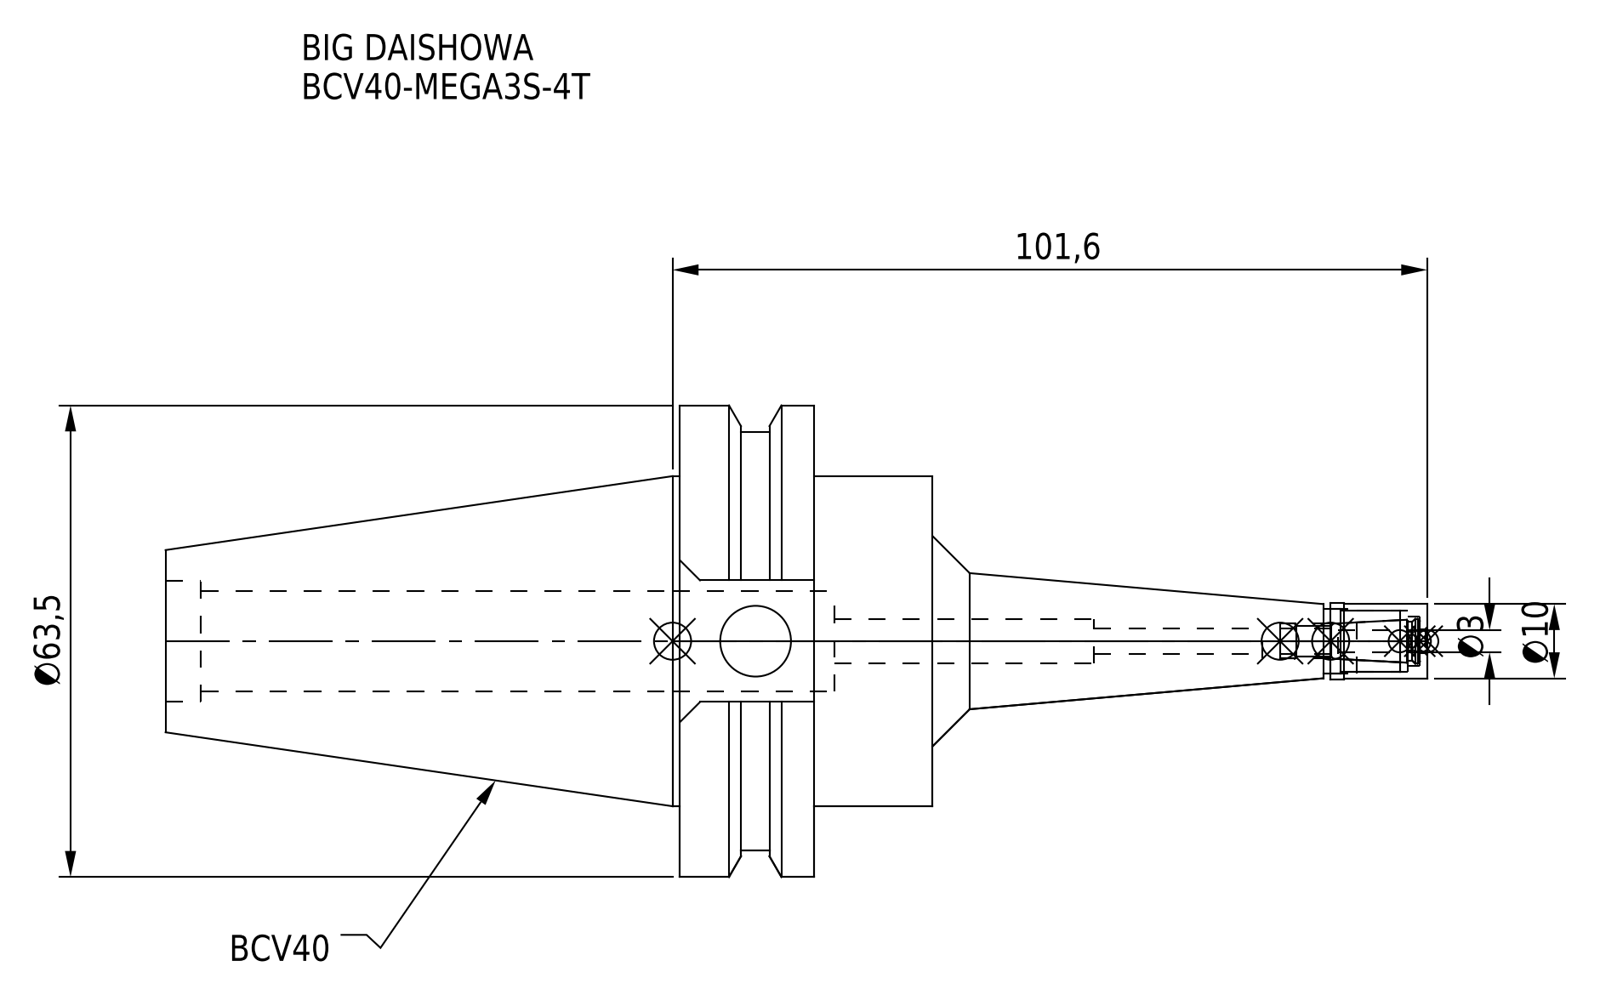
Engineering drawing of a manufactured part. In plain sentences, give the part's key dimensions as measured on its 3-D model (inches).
The part is named "BCV40-MEGA3S-4T-030.stp; BCV40-MEGA3S-4T_1.stp; BCV40-MEGA3S-4T; MGN3S_1.stp (+3 more)". Its 3-D file was written by "SolidWorks 2019 (CONFIG_CONTROL_DESIGN)". It is 2 solids with 86 faces: 32 planar, 40 cylindrical and 14 other. Overall it measures 6.687 by 2.5 by 2.415 inches. Its volume is 8.388 cubic inches and its surface area 42.61 square inches. Round holes: 1 of diameter 0.13, 1 of diameter 0.134, 1 of diameter 0.185, 1 of diameter 0.236, 1 of diameter 0.26, 1 of diameter 0.323, 1 of diameter 0.343, 1 of diameter 0.375, 1 of diameter 0.535, 1 of diameter 0.643. Round bosses or shafts: 1 of diameter 2.5, 1 of diameter 2.219, 1 of diameter 1.75, 1 of diameter 0.406, 1 of diameter 0.394. The main face-to-face distances are 0.711, 0.628, 1.339, 4.065, 3.437, 2.726, 1.872, 0.645, 0.106, 0.522.
